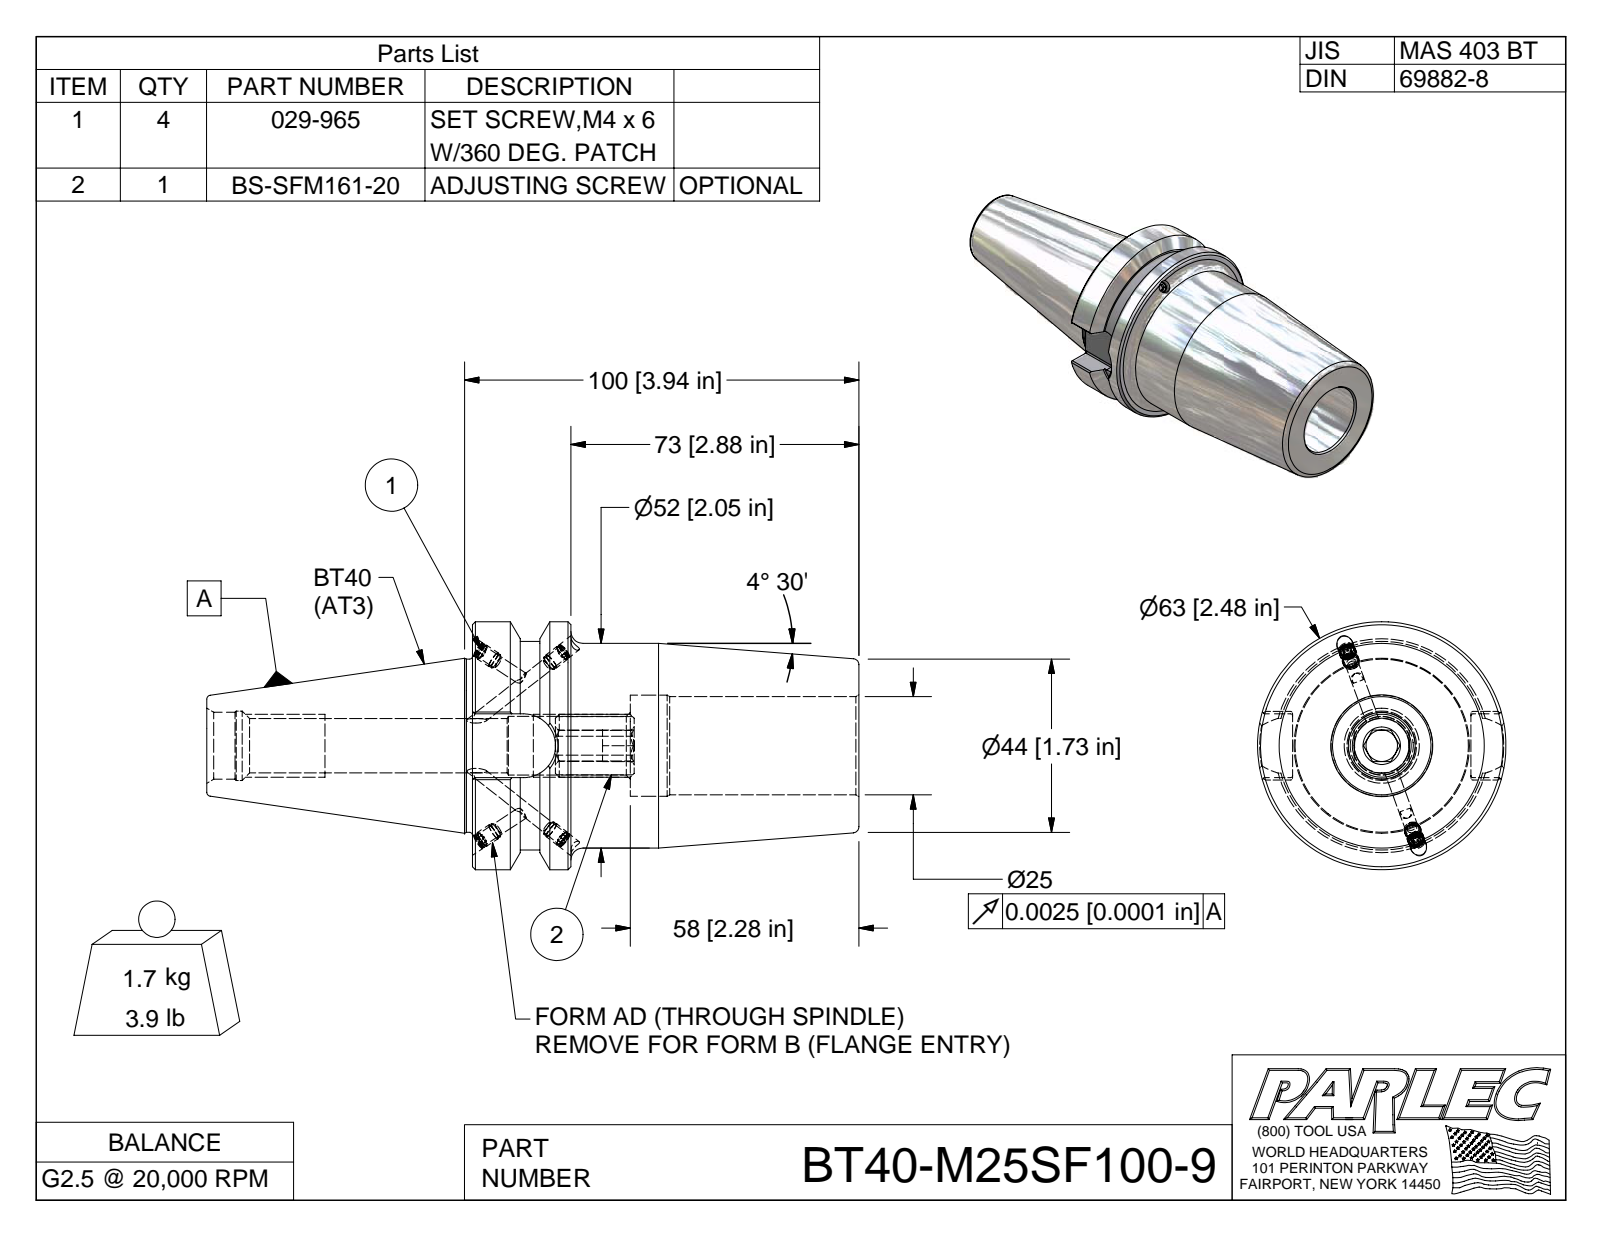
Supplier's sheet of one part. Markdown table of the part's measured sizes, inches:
| quantity | value |
| --- | --- |
| part name | BT40-M25SF100-9; BT40BC-M25SF100-9-1; 029-965; BS-SFM161-20 |
| STEP written by | Autodesk Inventor 2009 (AUTOMOTIVE_DESIGN) |
| units | inches |
| bodies | 6 solids, 173 faces (79 planar, 43 cylindrical, 51 other) |
| overall size | 6.512 × 2.48 × 2.48 |
| volume | 14 in³ |
| surface area | 63.72 in² |
| round holes (diameter × count) | 0.13 × 4, 0.161 × 4, 0.694 × 1, 0.983 × 1, 1.013 × 1 |
| round bosses / shafts (diameter × count) | 0.165 × 4, 0.157 × 4, 2.48 × 1, 2.087 × 1, 2.047 × 1, 1.75 × 1, 1.73 × 1 |
| partial cylindrical surfaces (radius × count) | 0.02 × 8, 0.315 × 1, 0.319 × 1 |
| main face-to-face distances | 3.859, 0.984, 2.875, 0.615, 1.166, 1.576, 0.592, 2.283, 1.78, 2.653 |
